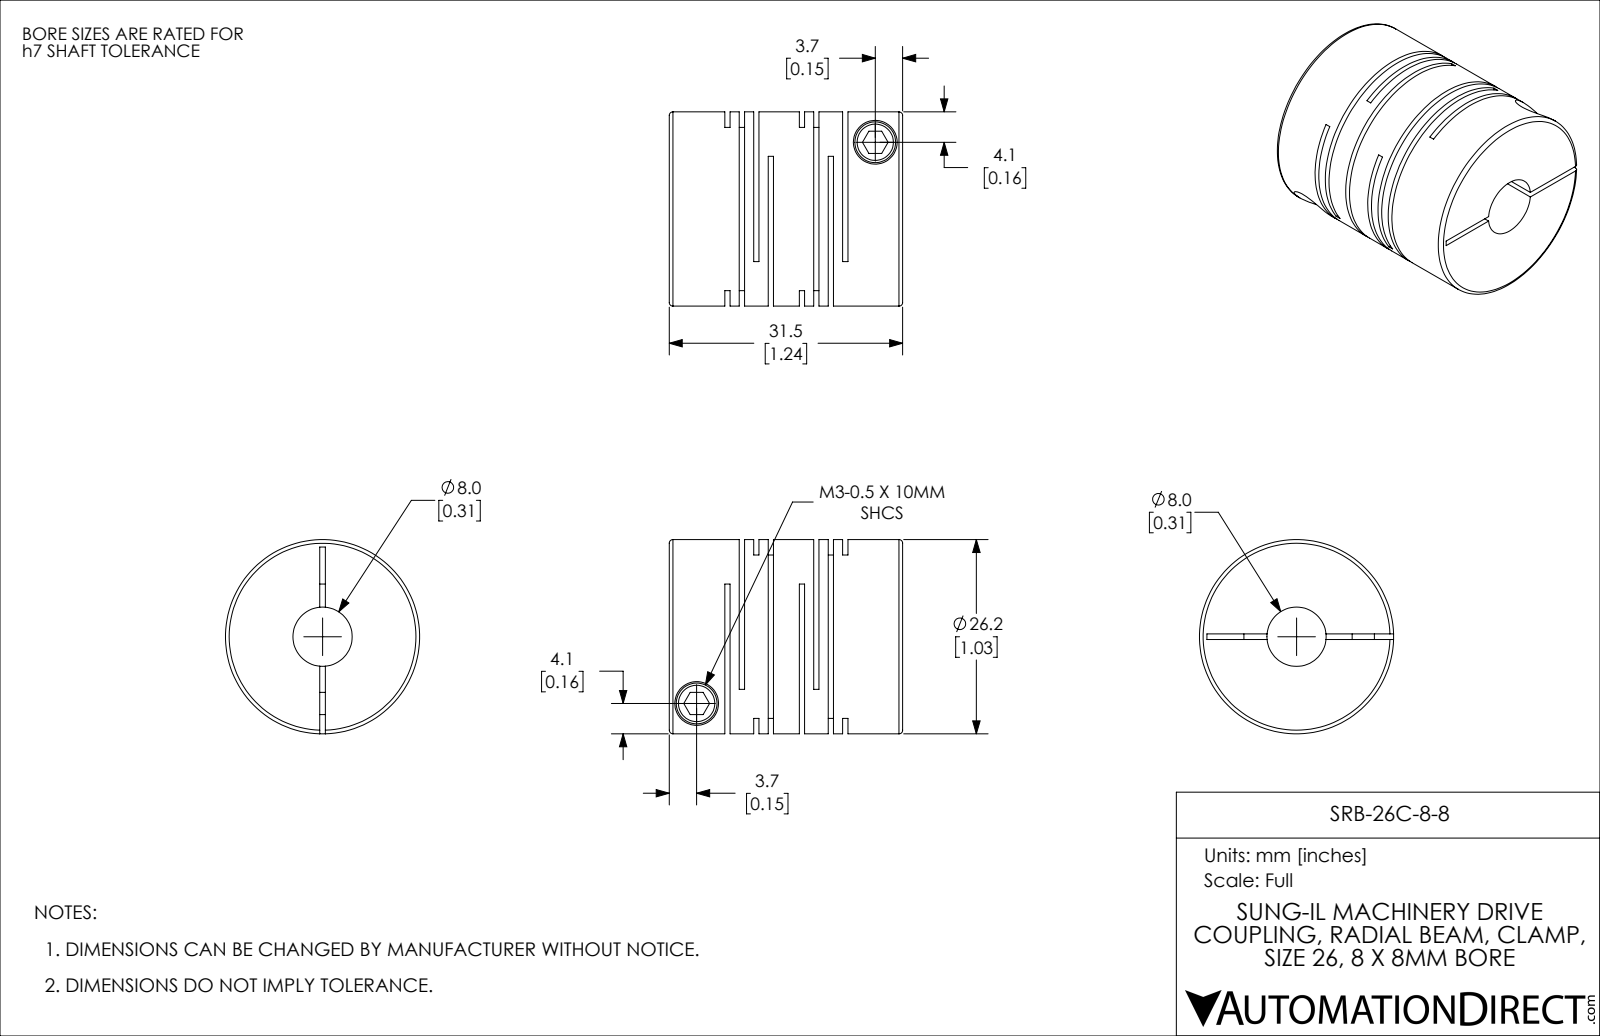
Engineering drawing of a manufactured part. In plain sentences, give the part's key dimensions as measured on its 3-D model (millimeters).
The part is named "SRB-26C-8-8". Its 3-D file was written by "SolidWorks 2021 (CONFIG_CONTROL_DESIGN)". It is 1 solid with 114 faces: 60 planar, 42 cylindrical and 12 other. Overall it measures 31.5 by 26.2 by 26.2 millimeters. Its volume is 12 651 cubic millimeters and its surface area 11 126 square millimeters. Round holes: 2 of diameter 3, 2 of diameter 5.9, 1 of diameter 8. Round bosses or shafts: 2 of diameter 5.5, 1 of diameter 26.2. The main face-to-face distances are 1.95, 10.05, 0.71, 3.9, 8.1, 12, 1.24, 2.66, 9.34, 13.95.
